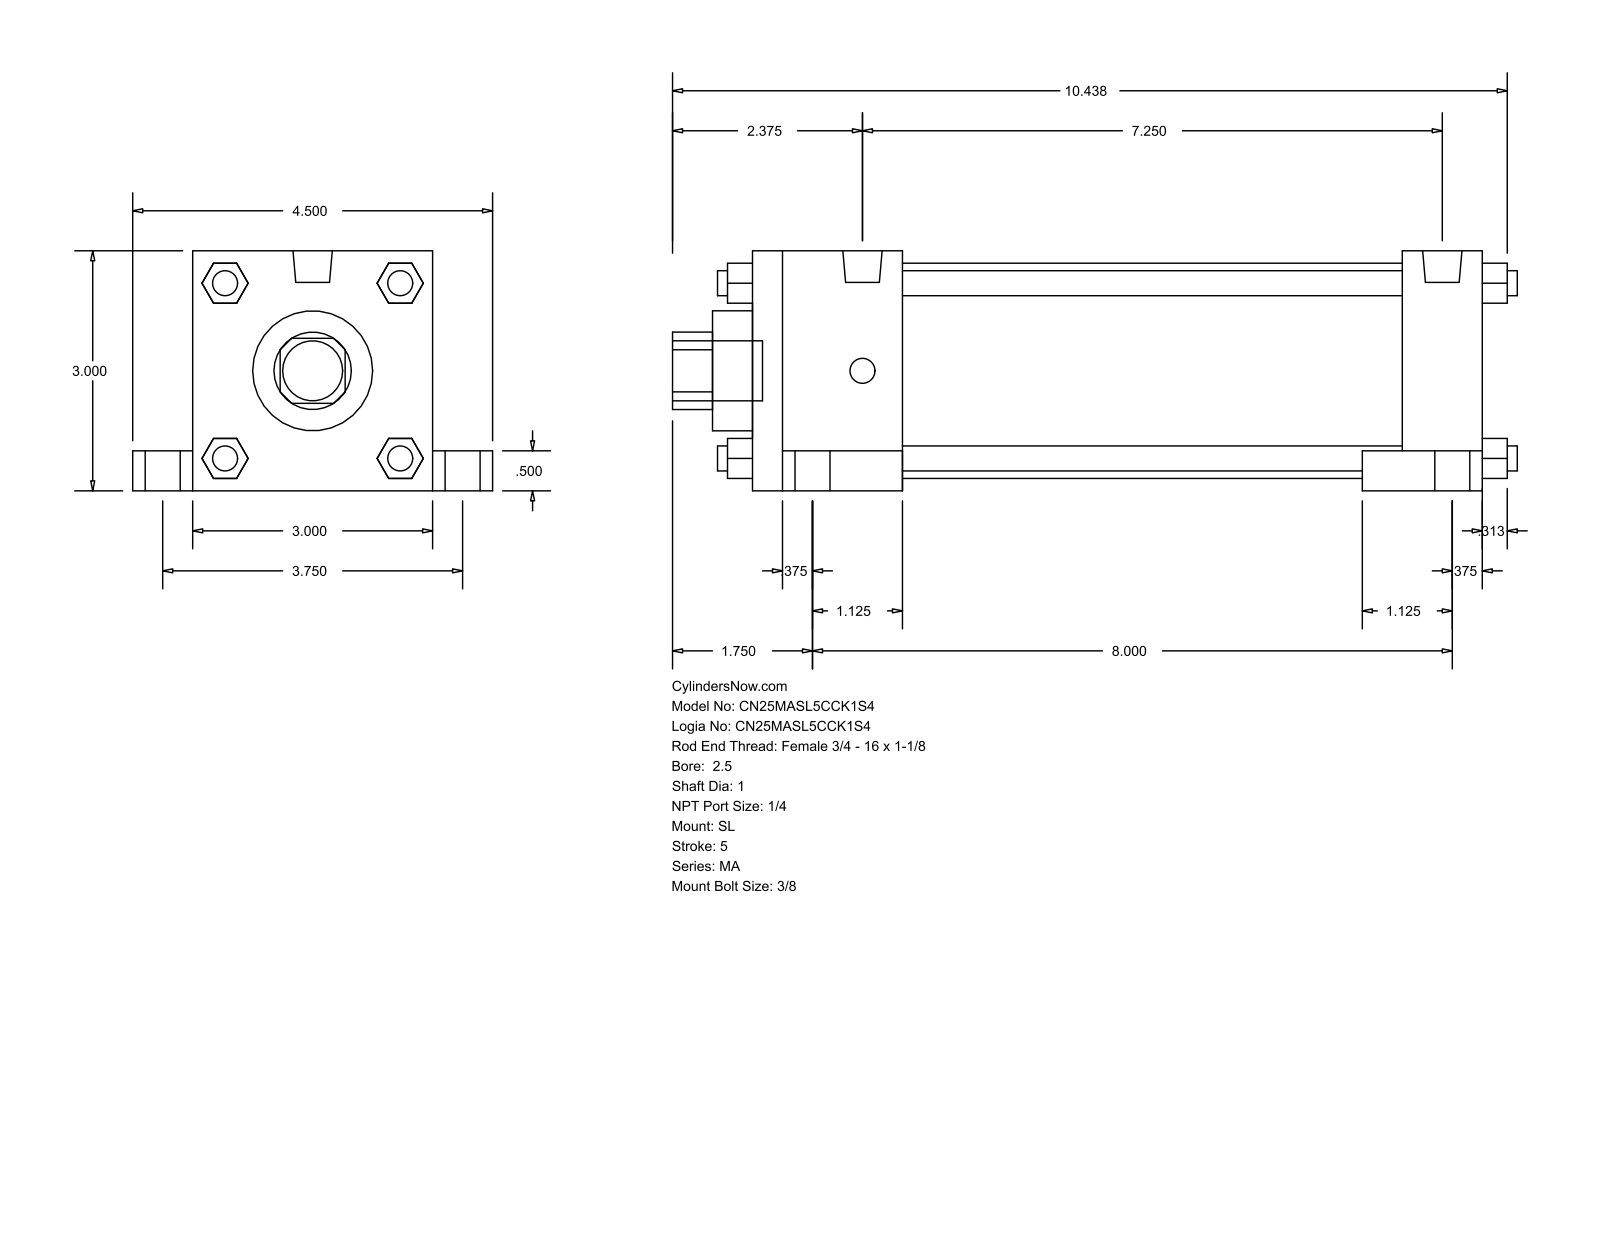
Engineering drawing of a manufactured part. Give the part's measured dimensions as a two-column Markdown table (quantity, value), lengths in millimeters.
| quantity | value |
| --- | --- |
| part name | MA_SL__0250_1 |
| STEP written by | GSSL Pune (CONFIG_CONTROL_DESIGN) |
| units | millimeters |
| bodies | 0 solids, 148 faces (112 planar, 36 cylindrical, 0 other) |
| overall size | 268.29 × 114.3 × 76.2 |
| round holes (diameter × count) | 25.4 × 1, 38.1 × 1, 68.33 × 1 |
| round bosses / shafts (diameter × count) | 7.94 × 8, 17.46 × 4, 11.11 × 4, 12.49 × 2, 19.05 × 1 |
| partial cylindrical surfaces (radius × count) | 12.29 × 1 |
| main face-to-face distances | 76.2, 231.78, 12.7, 158.75, 25.4, 47.63, 184.15, 206.38, 19.05, 95.25 |
